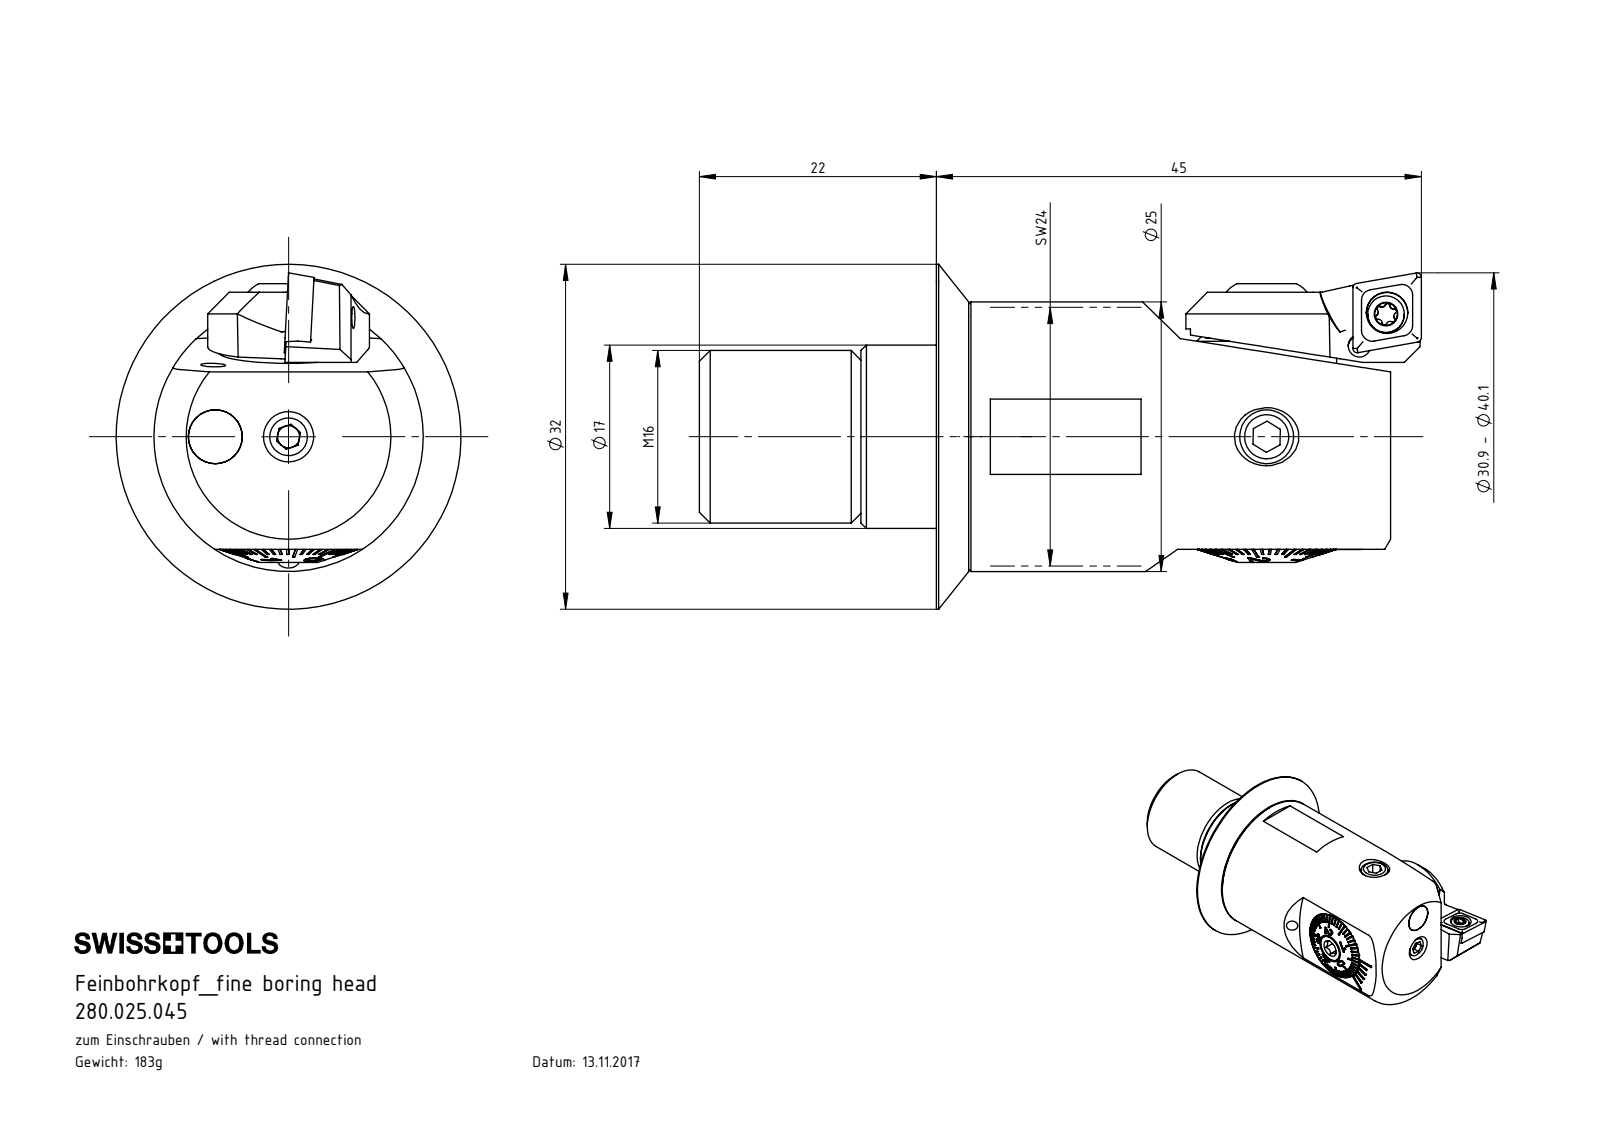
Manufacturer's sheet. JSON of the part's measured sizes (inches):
{"part_name": "Klebstoff D5; F25-BG2.008.009_A; HP5-F25.AA3.045_A_Aktuell 06.2014-180ø-M1x2 Abstand+0.7 versetzt 0.62; T7 M2.5 x 6_PreviewCfg (+8 more)", "step_written_by": "SolidWorks 2017 (AUTOMOTIVE_DESIGN)", "units": "inches", "bodies": {"solids": 14, "faces": 550, "planar": 319, "cylindrical": 64, "other": 167}, "overall_size": [2.565, 1.142, 1.142], "volume_in3": 1.689, "surface_area_in2": 21.08, "round_holes": [[0.059, 3], [0.098, 2], [0.13, 2], [0.165, 2], [0.081, 1], [0.094, 1], [0.106, 1], [0.118, 1], [0.197, 1], [0.217, 1], [0.252, 1], [0.287, 1]], "round_bosses_or_shafts": [[0.197, 2], [0.195, 2], [1.142, 1], [0.669, 1], [0.65, 1], [0.63, 1], [0.512, 1], [0.511, 1]], "partial_cylinders_radius": [[0.055, 4], [0.02, 2], [0.059, 2], [0.008, 1], [0.049, 1], [0.079, 1]], "face_to_face_distances": [1.659, 0.315, 0.059, 0.591, 0.154, 0.122, 0.032, 1.974, 0.063, 0.091], "hole_center_spacings": [0.268, 0.288]}
